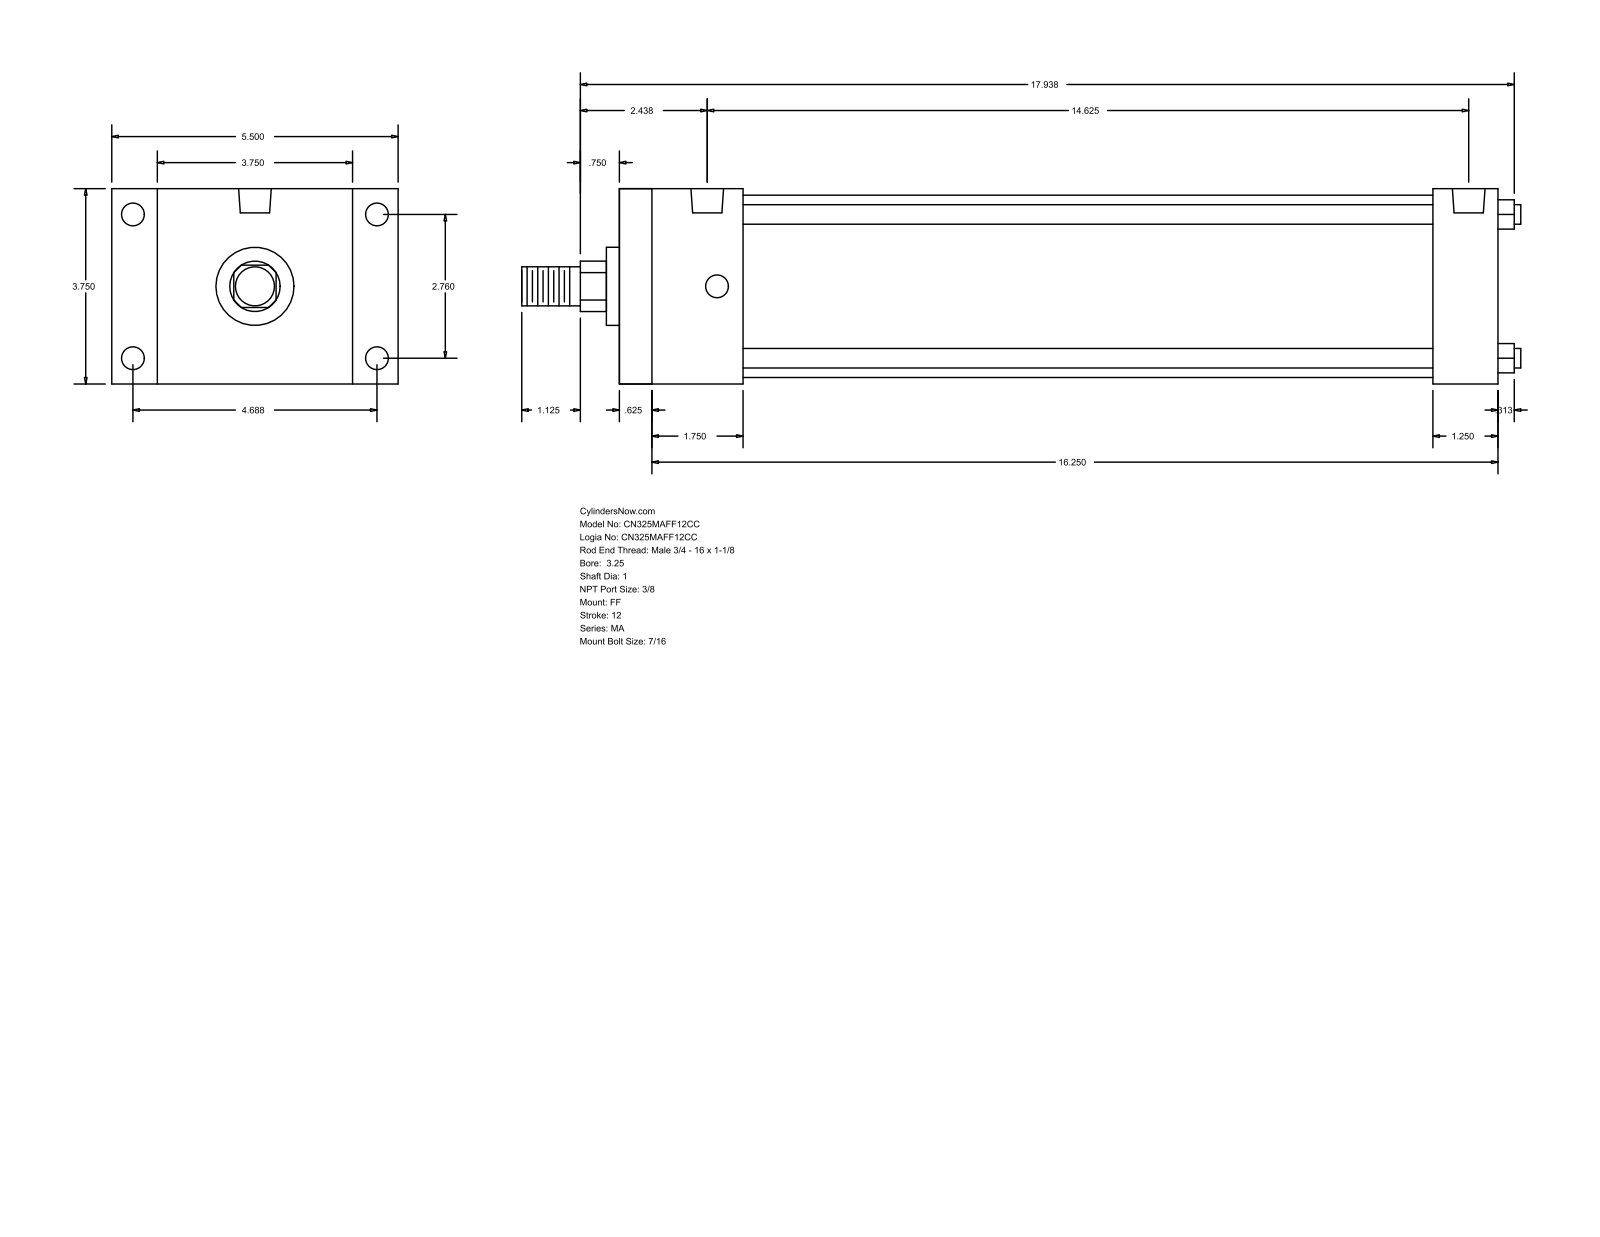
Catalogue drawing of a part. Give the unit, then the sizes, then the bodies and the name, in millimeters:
Units: millimetres
Overall size (bounding box): 487.36 × 139.7 × 95.25
Round holes (diameter × count): ⌀11.11 ×8, ⌀15.93 ×2
Round bosses / shafts (diameter × count): ⌀9.53 ×4, ⌀88.9 ×1, ⌀38.1 ×1, ⌀25.4 ×1, ⌀19.05 ×1
Partial cylindrical surfaces — rounded edges, fillets, slot ends (radius × count): R12.29 ×1
Main face-to-face distances: 95.24, 428.63, 15.87, 412.76, 22.23, 117.47, 60.33, 396.88, 44.46, 381.01
Hole centre spacings: 70.1, 119.06, 138.16, 361.95, 4.76, 4.77, 366.71, 366.72
Bodies: 0 solids, 92 faces (64 planar, 28 cylindrical, 0 other)
Part name (STEP PRODUCT): MA_FF__0325_1
STEP written by: GSSL Pune (CONFIG_CONTROL_DESIGN)
